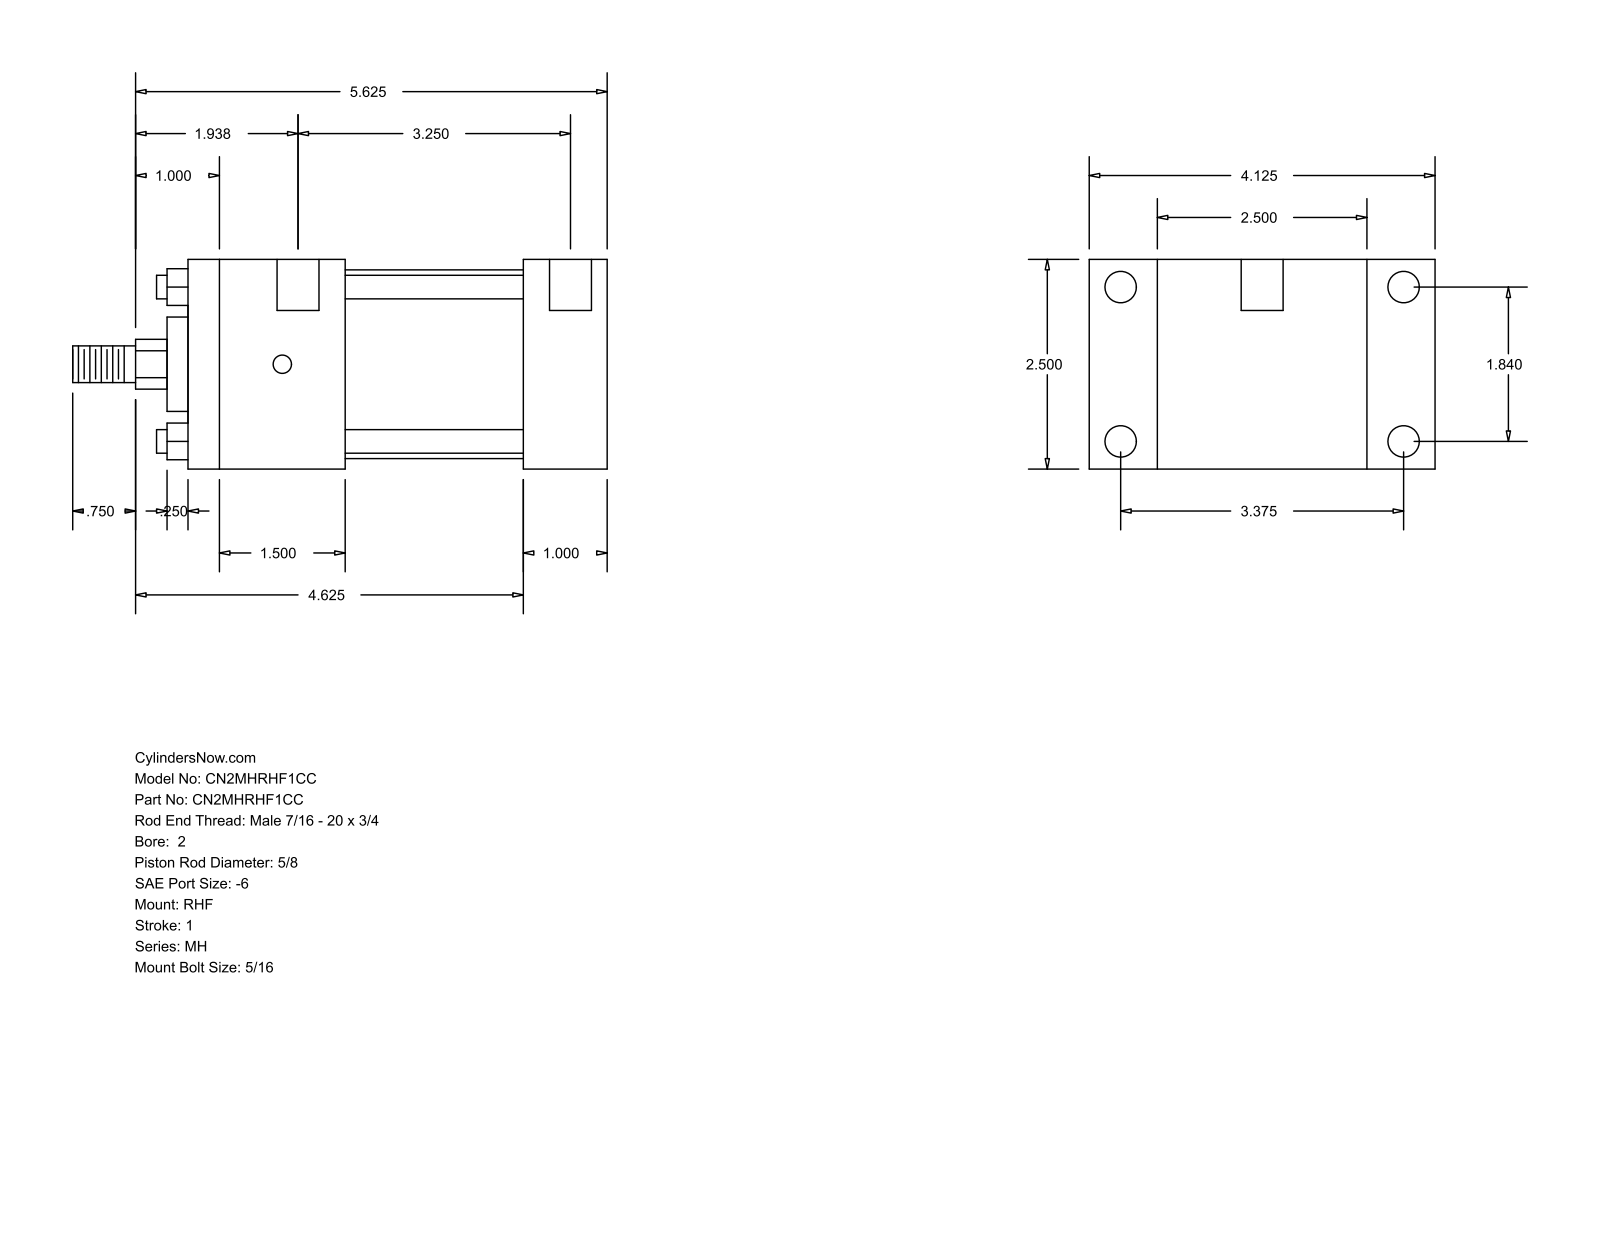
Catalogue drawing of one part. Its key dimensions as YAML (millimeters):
part_name: "MH_RHF__0200_0.625"
step_written_by: "GSSL Pune (CONFIG_CONTROL_DESIGN)"
units: millimeters
bodies: {solids: 0, faces: 88, planar: 60, cylindrical: 28, other: 0}
overall_size: [161.93, 104.78, 63.5]
round_holes:
  - {diameter: 5.56, count: 4}
  - {diameter: 9.53, count: 4}
  - {diameter: 12.7, count: 2}
round_bosses_or_shafts:
  - {diameter: 7.14, count: 4}
  - {diameter: 57.15, count: 1}
  - {diameter: 28.57, count: 1}
  - {diameter: 15.88, count: 1}
  - {diameter: 11.11, count: 1}
partial_cylinders:
  - {radius: 7.54, count: 1}
face_to_face_distances: [63.5, 25.41, 20.64, 84.14, 101.59, 127, 53.97, 104.78, 47.62, 79.38]
hole_center_spacings: [46.74, 85.72, 90.49, 97.63, 3.18, 4.76, 82.55, 85.73]
